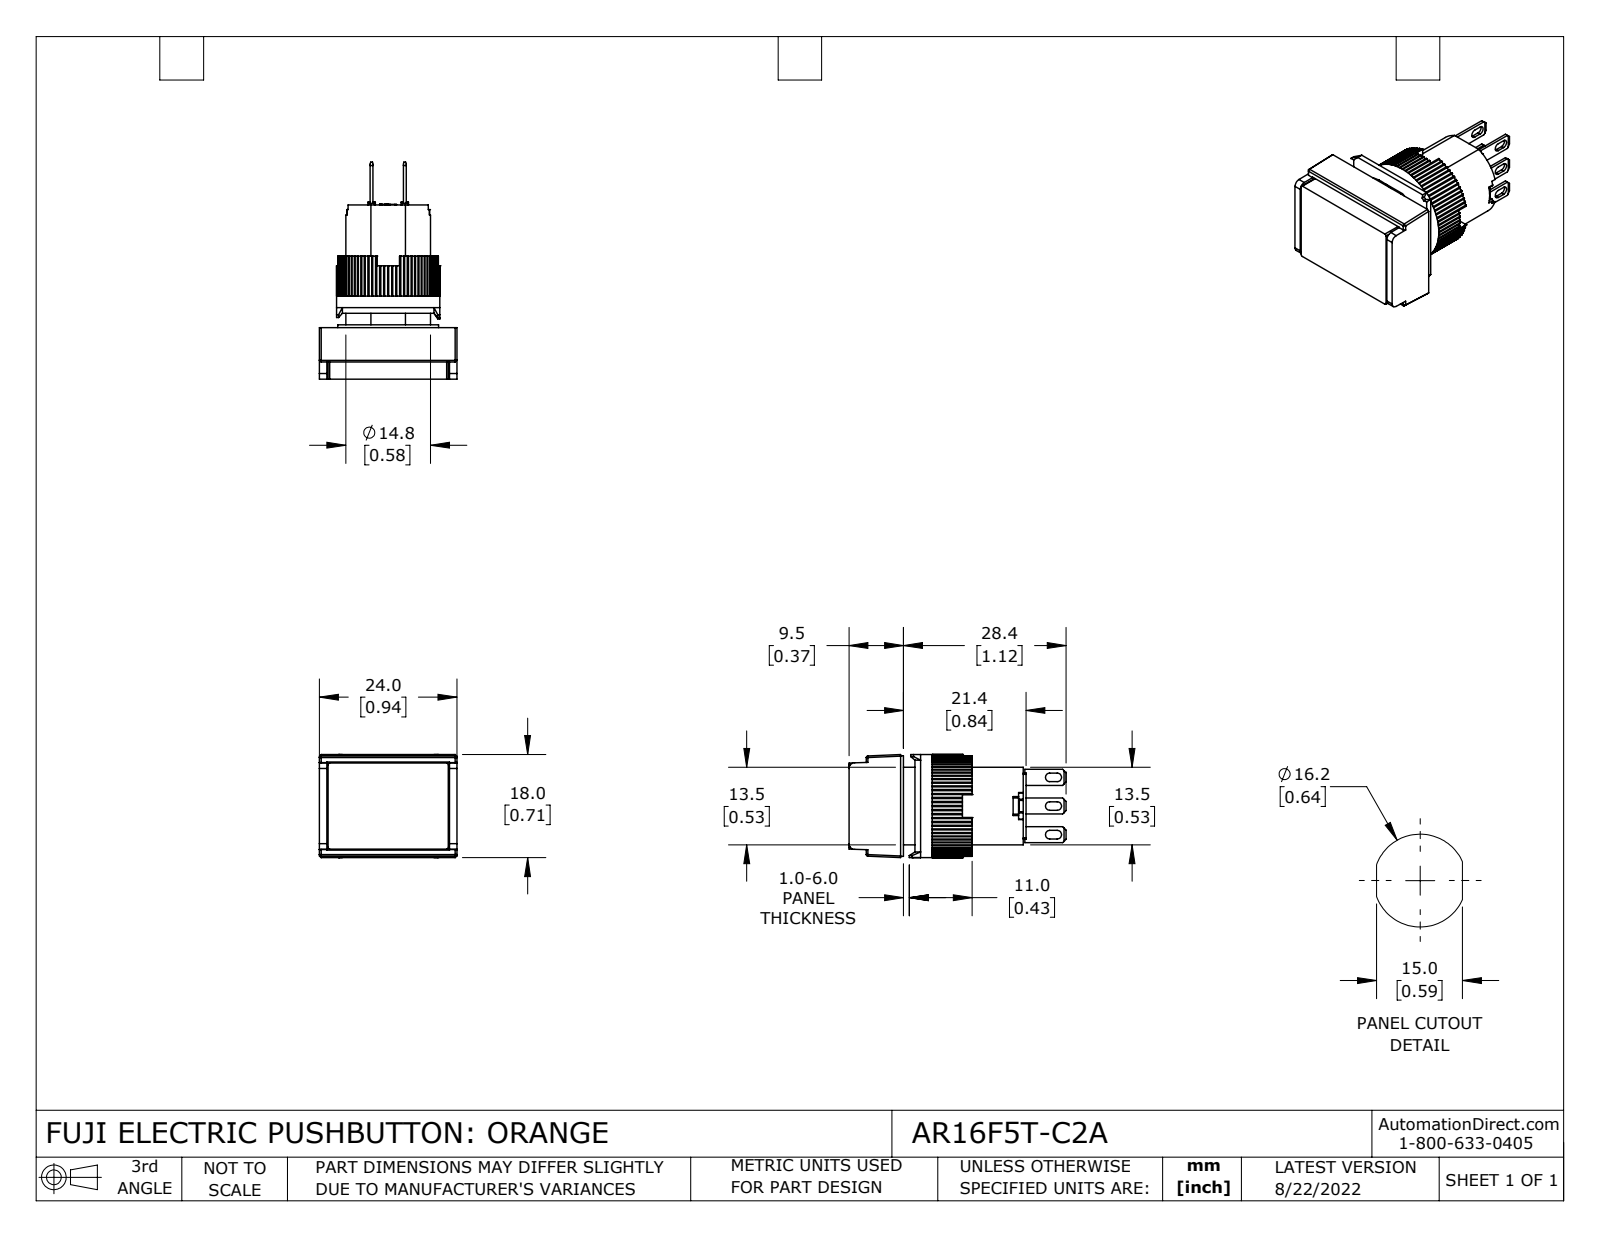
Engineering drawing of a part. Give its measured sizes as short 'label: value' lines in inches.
name: AR16F5T-C2A
written by: SolidWorks 2021 (CONFIG_CONTROL_DESIGN)
unit: in
bodies: 12 solids, 813 faces (632 planar, 177 cylindrical, 4 other)
size: 1.492 × 0.945 × 0.709
volume: 0.443 in³; area: 9.124 in²
holes: 1× ⌀0.543, 1× ⌀0.583
bosses: 1× ⌀0.709, 1× ⌀0.693
rounds: 80× R0.01, 12× R0.008, 6× R0.012, 6× R0.03, 2× R0.039
face distances: 0.213, 0.354, 0.142, 0.492, 0.35, 0.138, 0.02, 0.843, 0.059, 0.453
